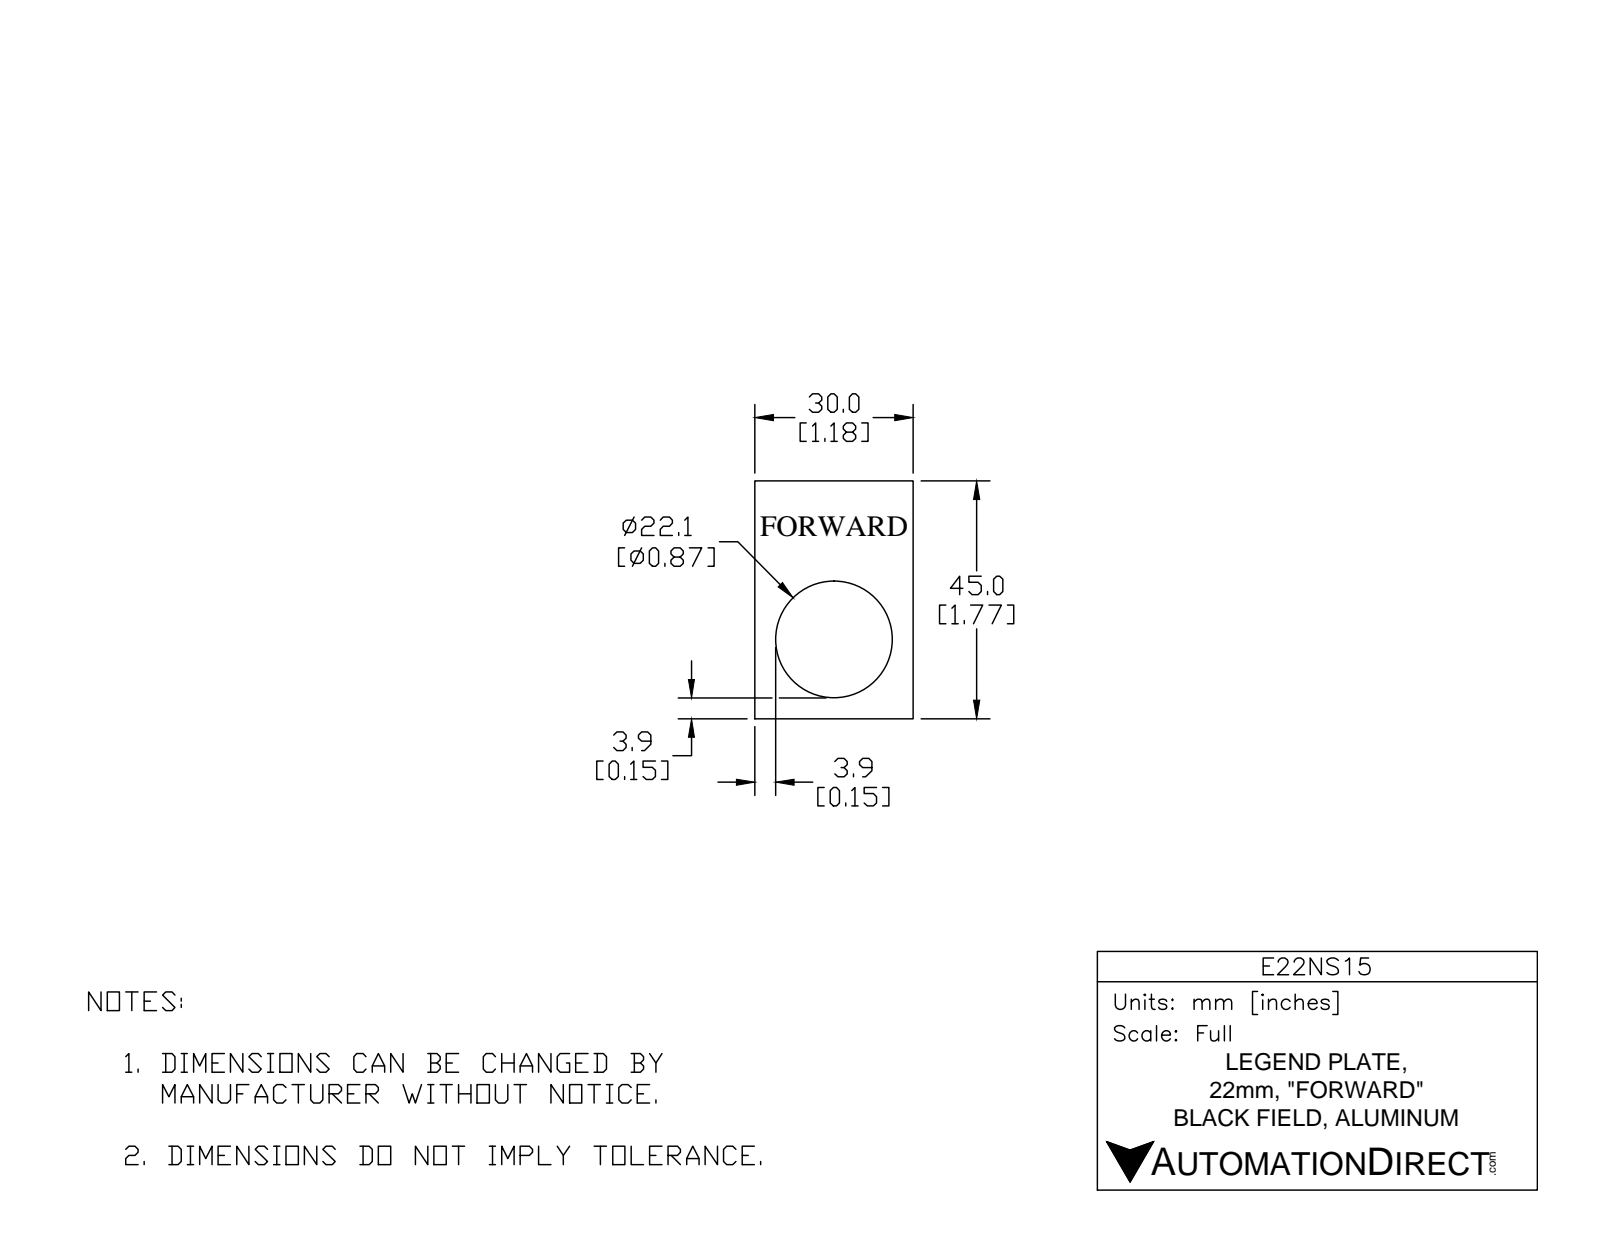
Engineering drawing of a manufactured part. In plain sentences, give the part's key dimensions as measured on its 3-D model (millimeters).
The part is named "E22NS15". Its 3-D file was written by "SolidWorks 2017 (AUTOMOTIVE_DESIGN)". It is 1 solid with 111 faces: 83 planar, 3 cylindrical and 25 other. Overall it measures 45 by 30 by 1.3 millimeters. Its volume is 1 248 cubic millimeters and its surface area 2 257 square millimeters. Round holes: 1 of diameter 22.2. The main face-to-face distances are 1.3, 30, 45, 1.05, 4.7, 40.3, 0.36, 0.35, 20.2, 23.59.
